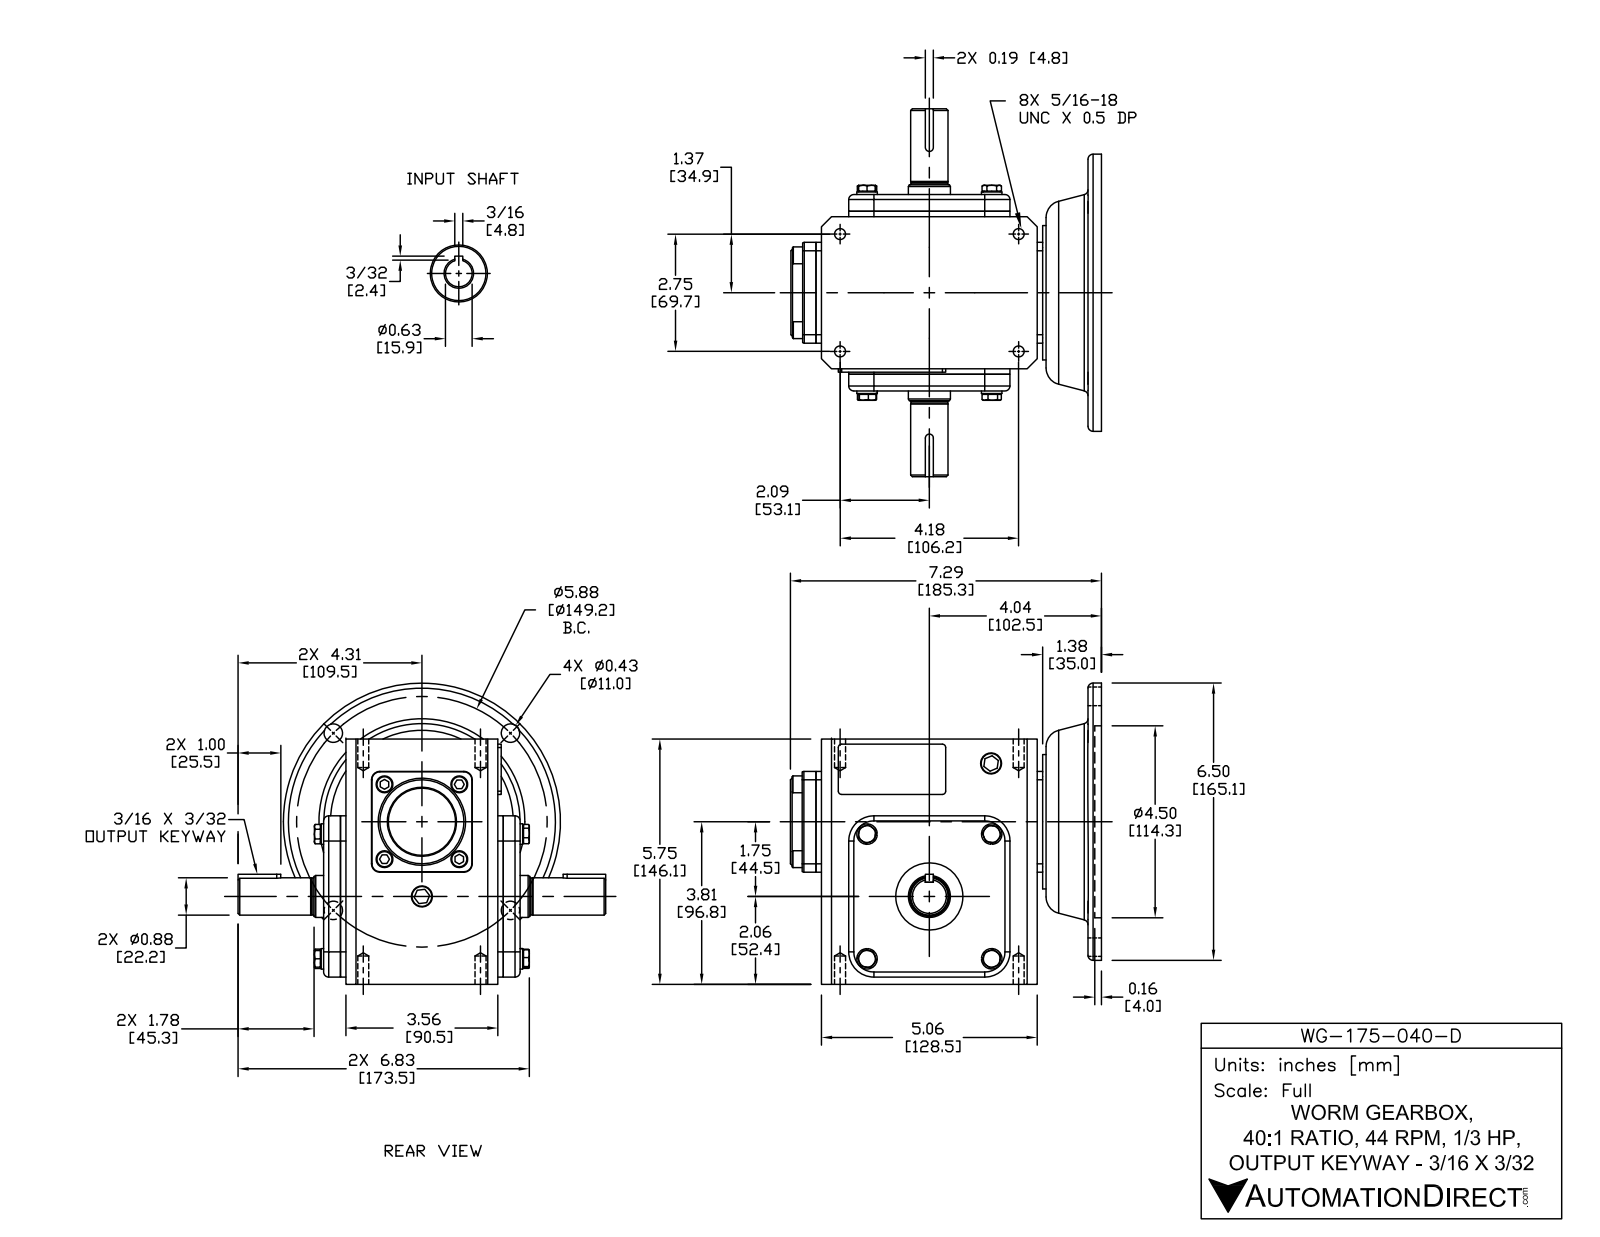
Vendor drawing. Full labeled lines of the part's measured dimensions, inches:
Part name (STEP PRODUCT): WG-175-040-D
STEP written by: SolidWorks 2015 (CONFIG_CONTROL_DESIGN)
Units: inches
Bodies: 45 solids, 647 faces (324 planar, 186 cylindrical, 137 other)
Overall size (bounding box): 8.622 × 7.283 × 7.06
Volume: 133.1 in³ · Surface area: 375.6 in²
Round holes (diameter × count): ⌀0.257 ×4, ⌀0.406 ×4, ⌀0.512 ×1, ⌀0.625 ×1, ⌀0.984 ×1, ⌀1.181 ×1, ⌀1.457 ×1, ⌀1.575 ×1, ⌀3.543 ×1, ⌀4.5 ×1
Round bosses / shafts (diameter × count): ⌀0.394 ×8, ⌀0.48 ×4, ⌀0.512 ×2, ⌀6.496 ×1, ⌀3.15 ×1, ⌀2.047 ×1, ⌀1.575 ×1, ⌀0.875 ×1
Partial cylindrical surfaces — rounded edges, fillets, slot ends (radius × count): R0.079 ×8, R0.118 ×8, R0.197 ×4, R0.591 ×4, R0.02 ×2, R0.039 ×2, R0.094 ×2
Main face-to-face distances: 0.128, 3.819, 4.213, 0.394, 4.085, 3.691, 0.522, 0.315, 5.75, 6.693
Hole centre spacings: 2.937, 4.154, 2.103, 2.75, 4.188, 4.354, 5.01, 5.875
